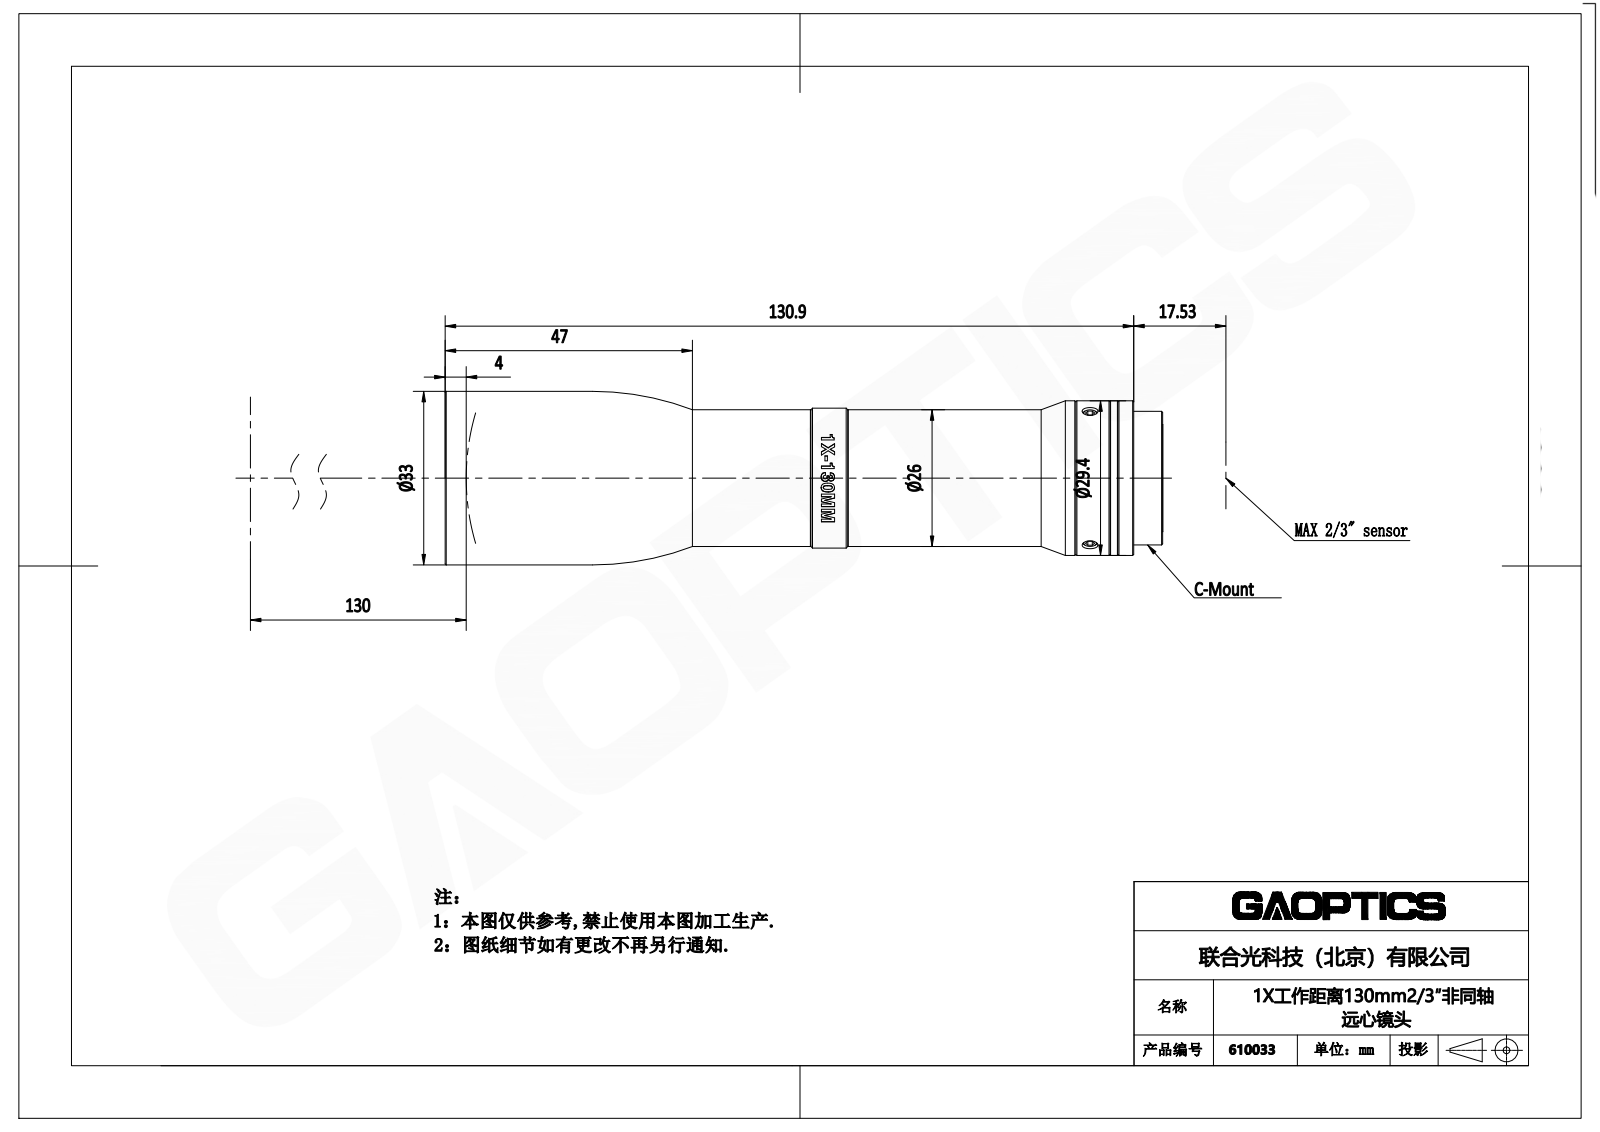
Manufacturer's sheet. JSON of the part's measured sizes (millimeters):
{"part_name": "610033", "step_written_by": "SolidWorks 2016 (AUTOMOTIVE_DESIGN)", "units": "millimeters", "bodies": {"solids": 1, "faces": 201, "planar": 43, "cylindrical": 60, "other": 98}, "overall_size": [136.4, 33, 33], "volume_mm3": 76685, "surface_area_mm2": 15009, "round_holes": [[20.5, 1], [23.9, 1], [29.9, 1]], "round_bosses_or_shafts": [[33, 1], [29.4, 1], [26.6, 1], [26, 1], [25.4, 1], [24.6, 1]], "partial_cylinders_radius": [[13.2, 1]], "face_to_face_distances": [121.6, 133.6, 12, 128.1, 6.5, 5.5, 2.8, 124.4, 130.9, 136.4]}
